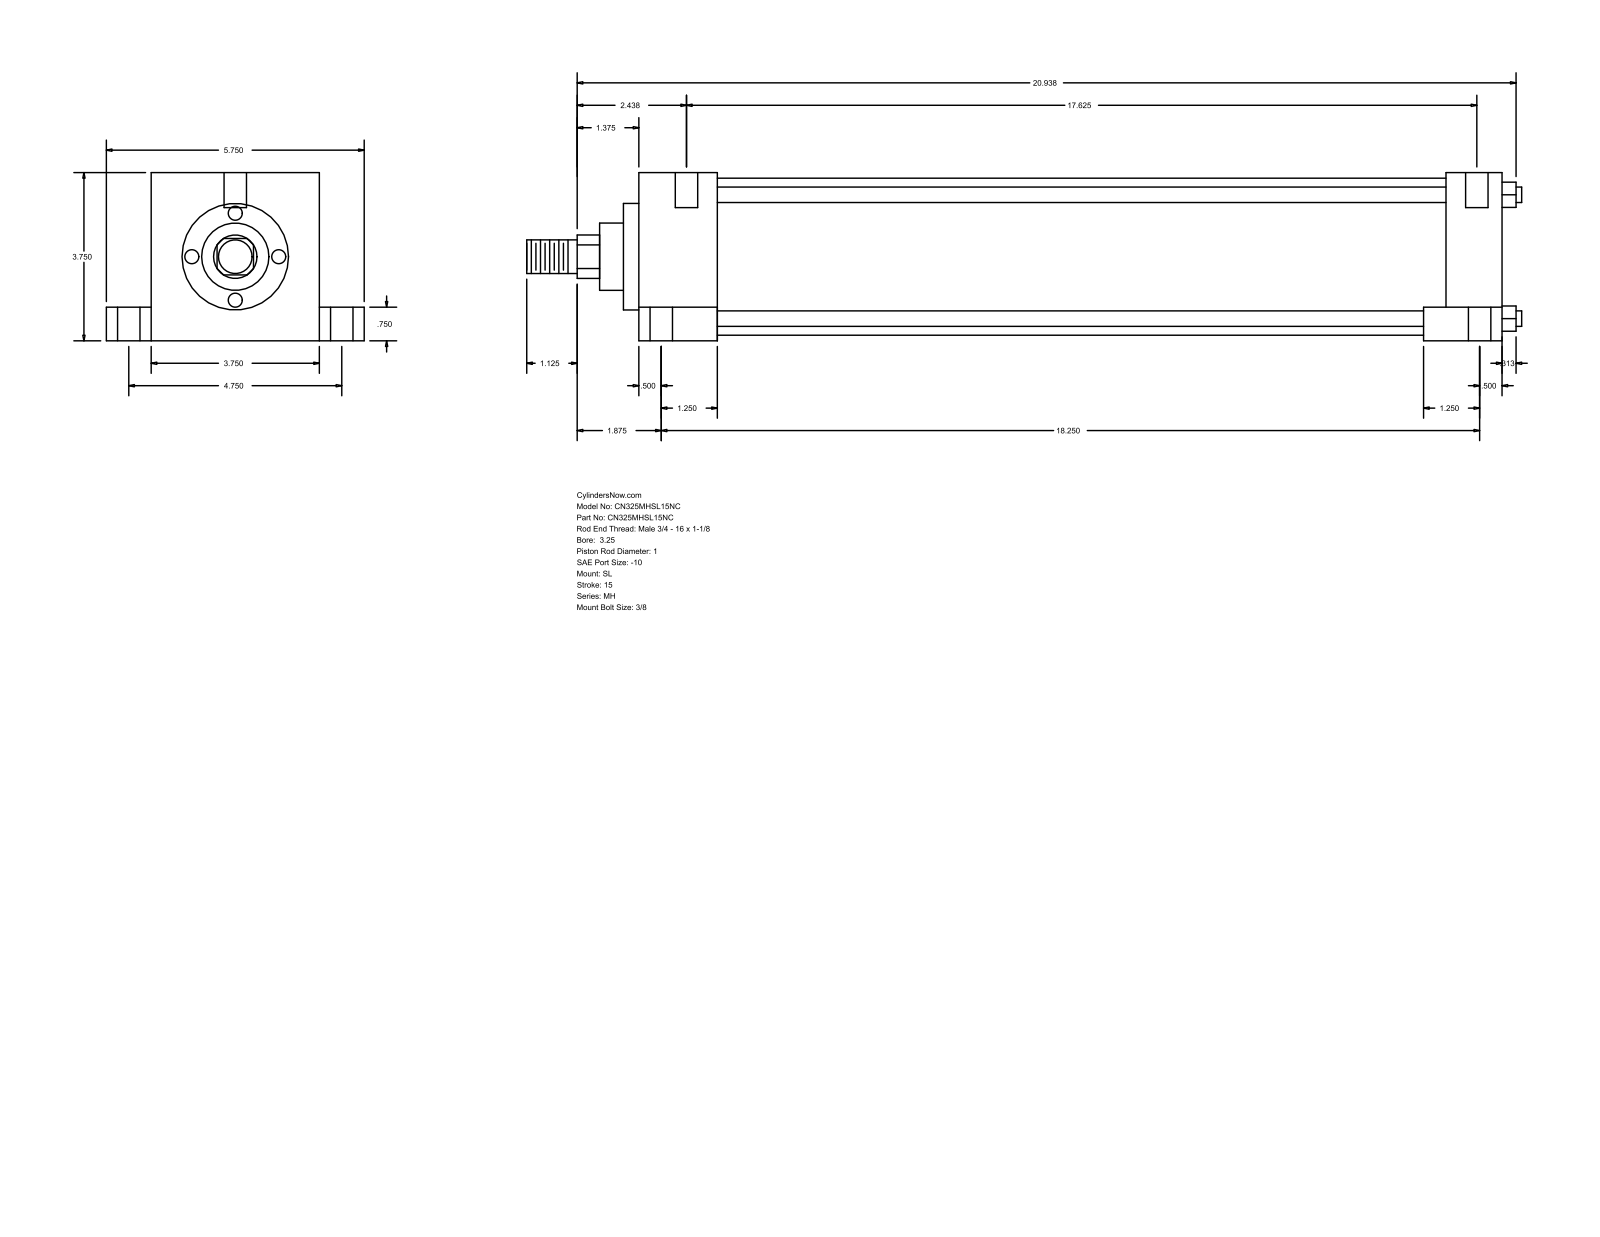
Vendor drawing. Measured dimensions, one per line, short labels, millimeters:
name: MH_SL__0325_1
written by: GSSL Pune (CONFIG_CONTROL_DESIGN)
unit: mm
bodies: 0 solids, 110 faces (77 planar, 33 cylindrical, 0 other)
size: 563.56 × 146.05 × 95.25
holes: 6× ⌀12.7, 4× ⌀5.56, 4× ⌀19.05
bosses: 4× ⌀8.76, 1× ⌀88.9, 1× ⌀60.33, 1× ⌀38.1, 1× ⌀25.4, 1× ⌀19.05
rounds: 1× R12.29
face distances: 95.24, 488.96, 44.46, 444.5, 25.41, 120.65, 19.05, 76.19, 457.2, 412.74
hole spacings: 60.35, 60.41, 61.65, 62, 120.66, 453.3, 454.02, 454.87
